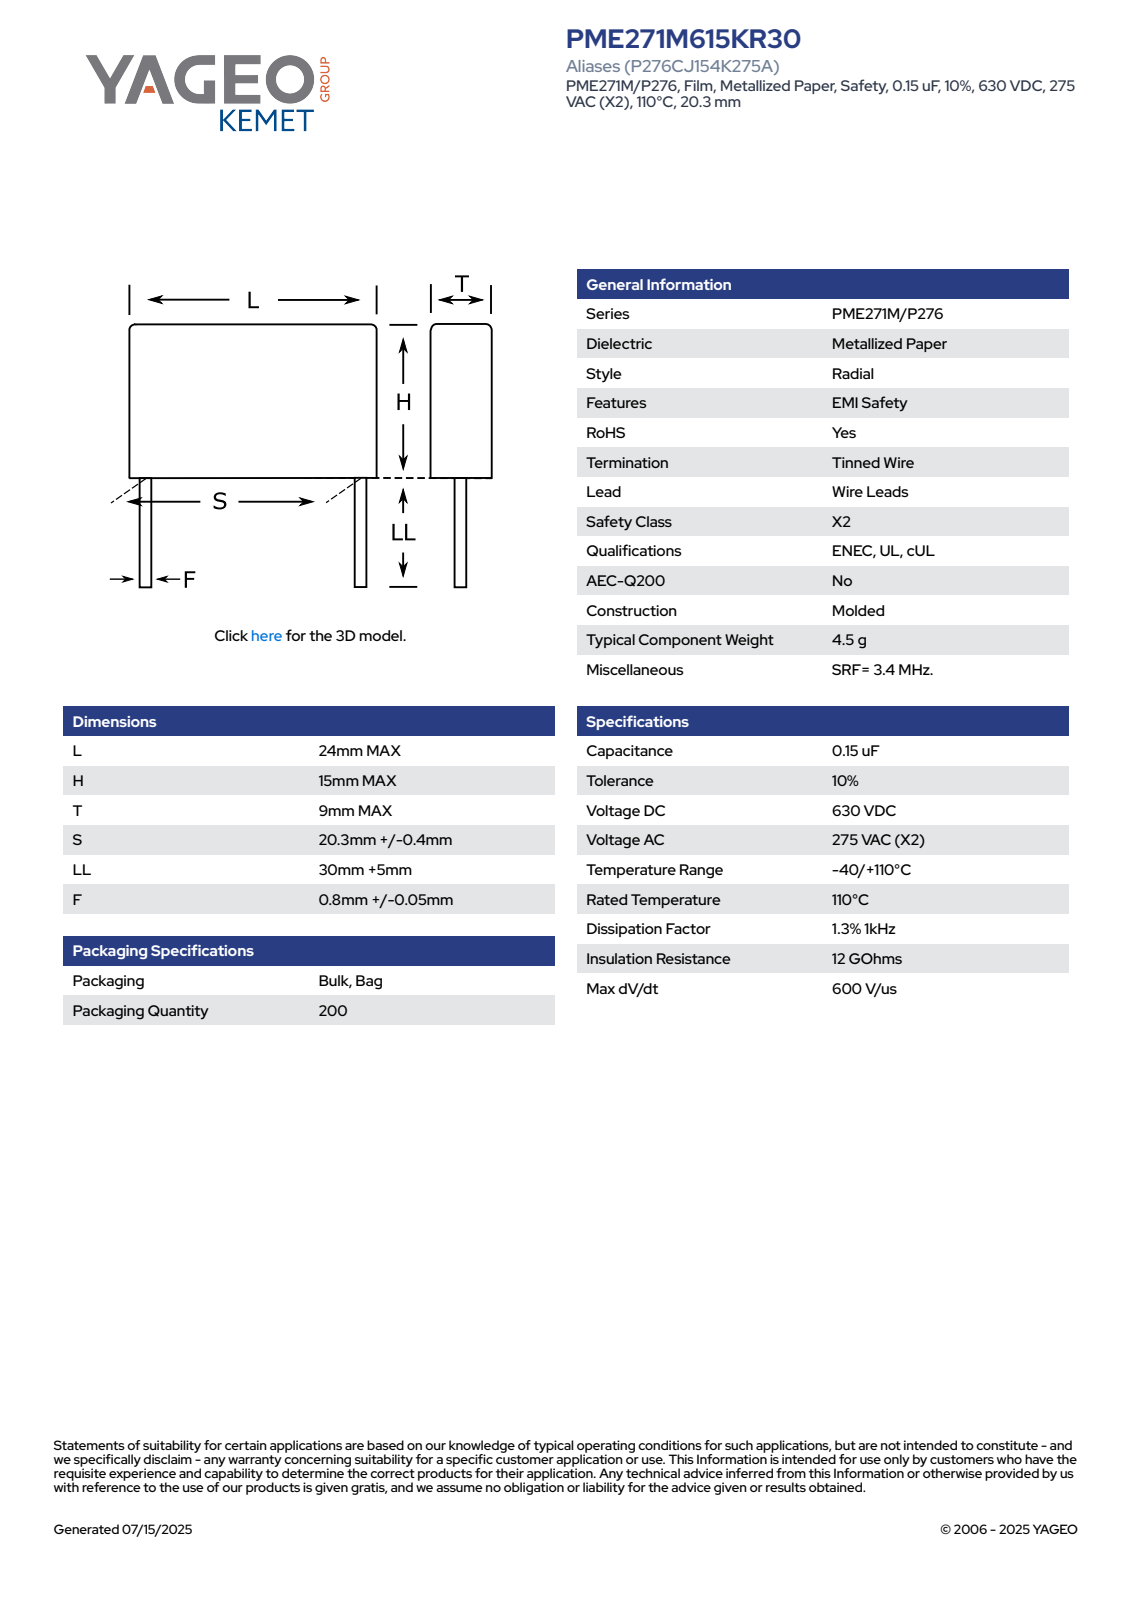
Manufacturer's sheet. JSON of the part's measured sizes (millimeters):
{"part_name": "CFR_MOLDED_24X15X9_L24H15T9S20.3LL35F0.8", "step_written_by": "SolidWorks 2014 (AUTOMOTIVE_DESIGN)", "units": "millimeters", "bodies": {"solids": 4, "faces": 73, "planar": 65, "cylindrical": 8, "other": 0}, "overall_size": [50, 24, 9.01], "volume_mm3": 3272, "surface_area_mm2": 1611, "round_bosses_or_shafts": [[0.8, 2]], "partial_cylinders_radius": [[0.5, 4]], "face_to_face_distances": [9, 15, 24, 35, 50, 43.44, 8.44, 6.56, 41.29, 6.29]}
